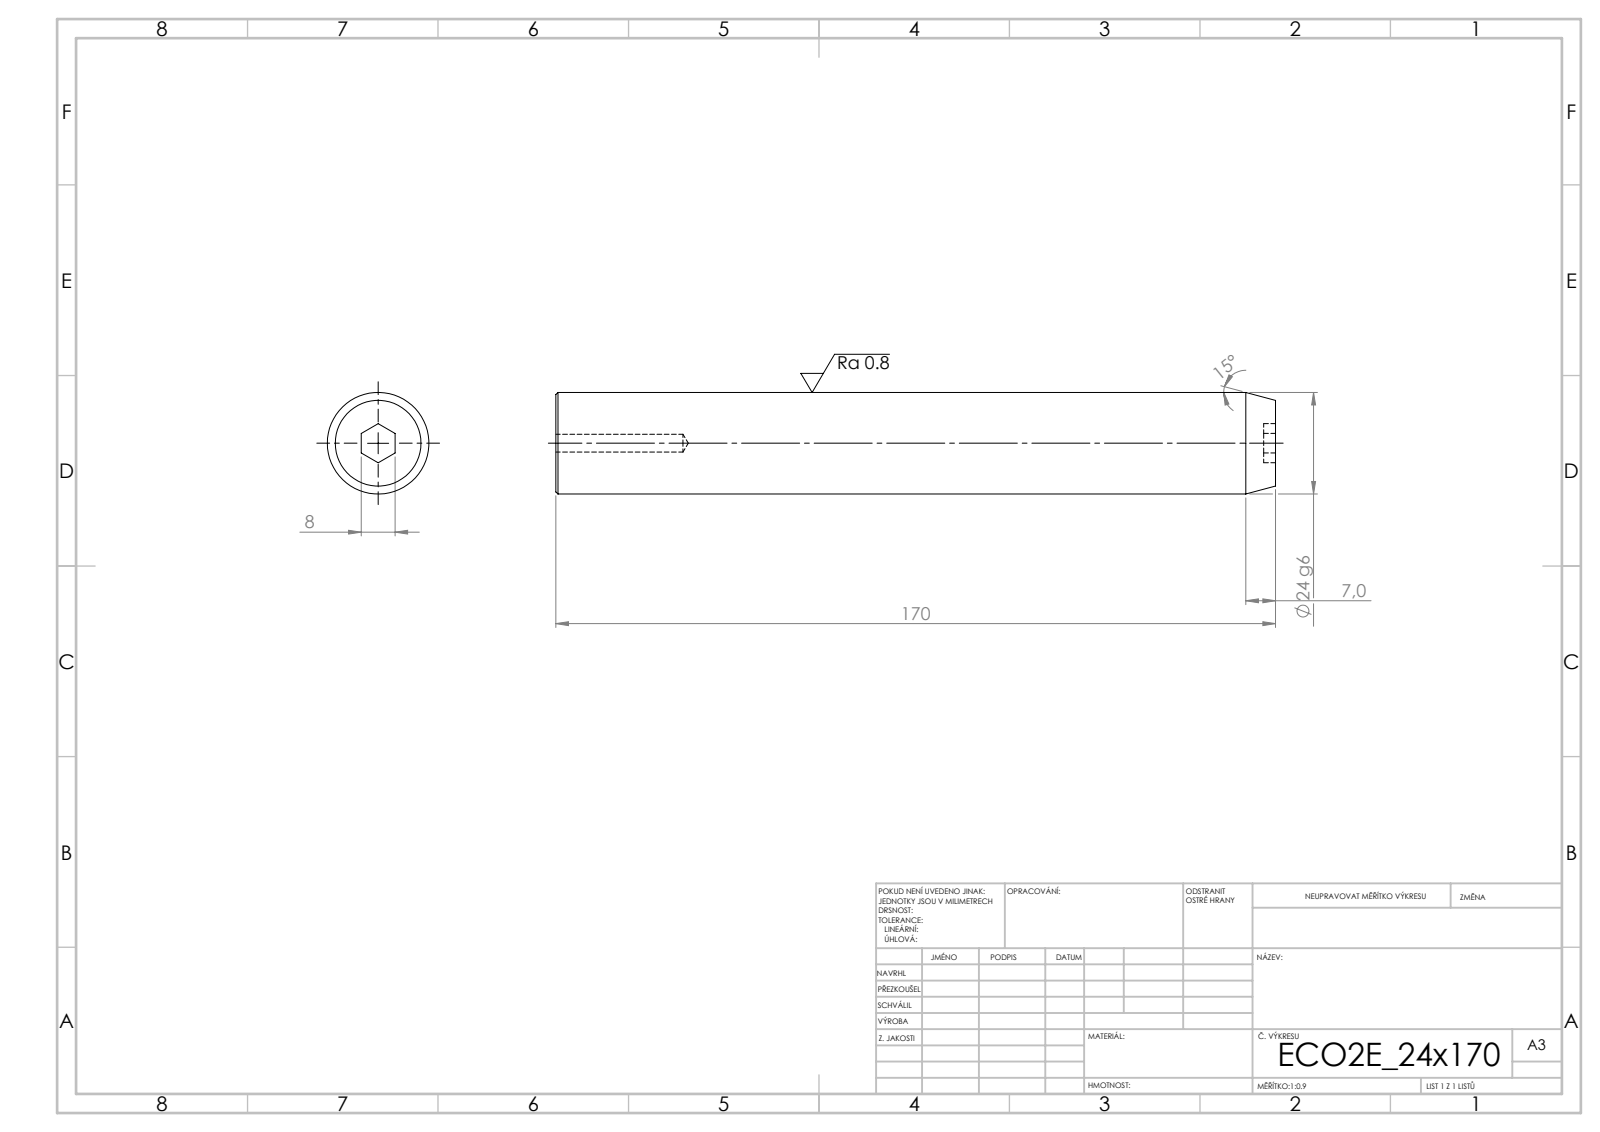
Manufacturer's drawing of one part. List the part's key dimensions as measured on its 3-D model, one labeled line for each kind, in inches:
STEP written by: SolidWorks 2019 (CONFIG_CONTROL_DESIGN)
Units: inches
Bodies: 1 solid, 19 faces (9 planar, 4 cylindrical, 6 other)
Overall size (bounding box): 6.693 × 0.945 × 0.945
Volume: 4.629 in³ · Surface area: 21.73 in²
Round holes (diameter × count): ⌀0.165 ×1
Round bosses / shafts (diameter × count): ⌀0.945 ×1
Main face-to-face distances: 6.693, 0.11, 6.583, 0.315
